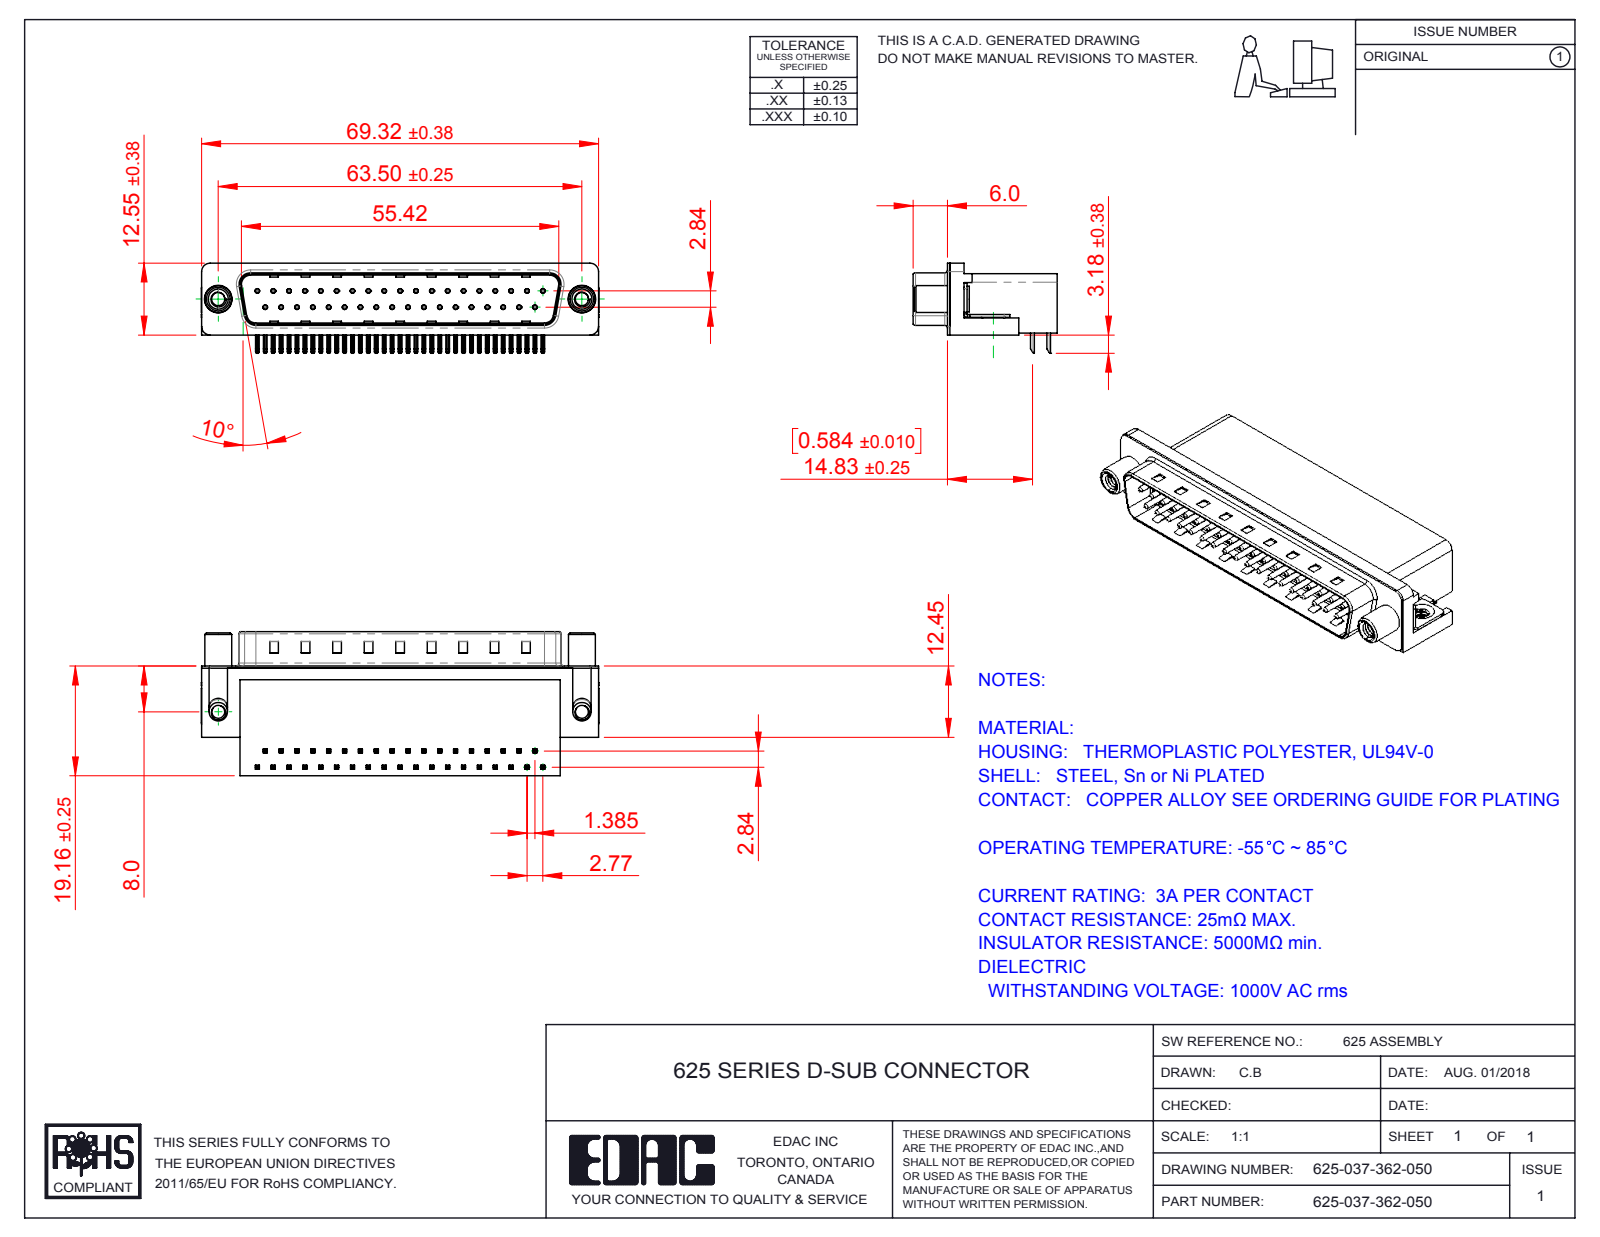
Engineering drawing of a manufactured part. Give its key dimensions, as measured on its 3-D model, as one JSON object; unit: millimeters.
{"part_name": "625 Shell_37 Socket; 625 Round Threaded Standoff; 625 Contact Bottom; 625-037-362-050 (+3 more)", "step_written_by": "SolidWorks 2016 (CONFIG_CONTROL_DESIGN)", "units": "millimeters", "bodies": {"solids": 43, "faces": 3227, "planar": 2007, "cylindrical": 937, "other": 283}, "overall_size": [69.4, 25.16, 15.73], "volume_mm3": 12702, "surface_area_mm2": 12033, "round_holes": [[0.35, 37], [0.8, 37], [2.26, 2], [2.3, 2], [3.1, 2], [4, 2], [4.8, 2], [5, 2]], "round_bosses_or_shafts": [[0.75, 37], [4.9, 2], [4.7, 2], [4.5, 2], [3.85, 2], [3.26, 2]], "partial_cylinders_radius": [[0.25, 148], [0.12, 74], [1, 16], [0.5, 9], [1.6, 8], [1.5, 7], [0.9, 4], [2, 4]], "face_to_face_distances": [10.34, 0.4, 18.76, 8.76, 2.84, 19.16, 2.09, 10.1, 1.74, 8.36], "hole_center_spacings": [3.16, 2.77, 5.54, 8.31, 11.08, 13.85, 19.39, 22.16]}
